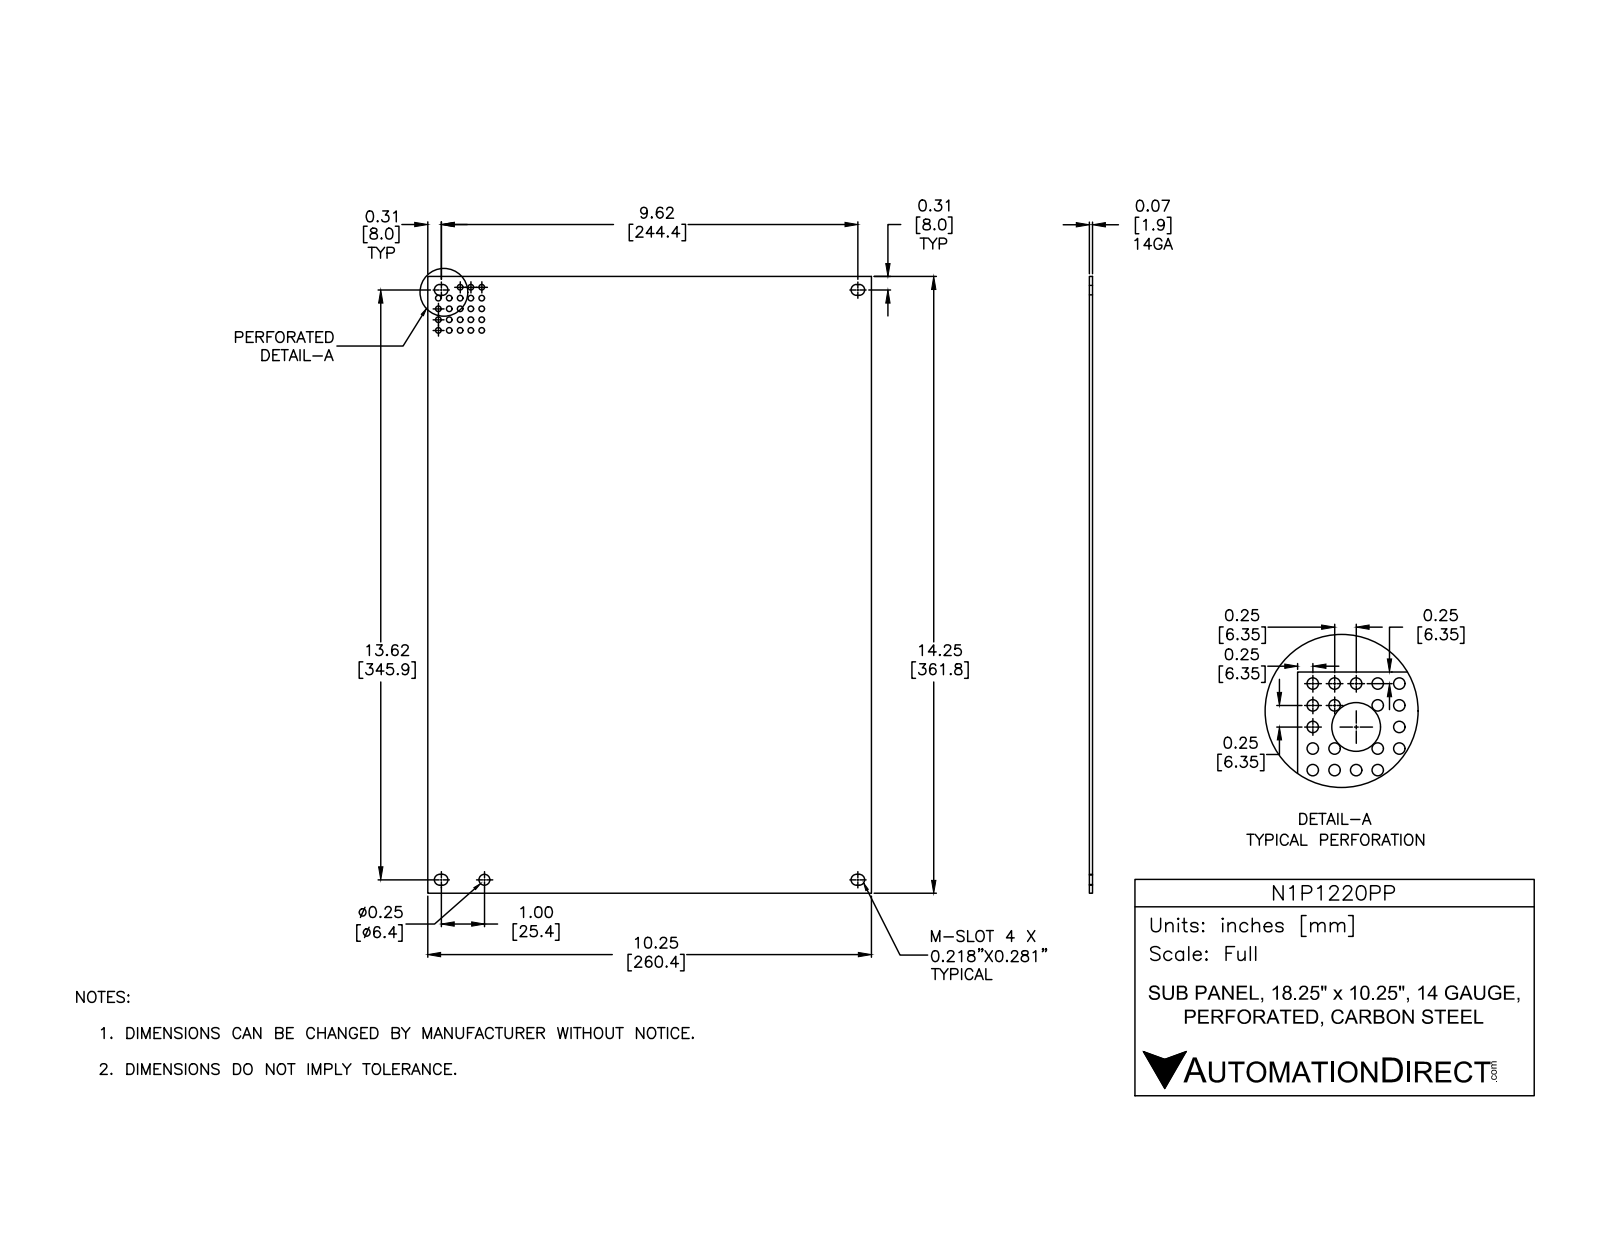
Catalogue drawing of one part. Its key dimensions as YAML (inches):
part_name: "N1P1220PP"
step_written_by: "Autodesk Inventor 2012 (AUTOMOTIVE_DESIGN)"
units: inches
bodies: {solids: 1, faces: 23, planar: 14, cylindrical: 9, other: 0}
overall_size: [18.25, 10.25, 0.074]
volume: 13.82
surface_area: 378.1
round_holes:
  - {diameter: 0.25, count: 1}
partial_cylinders:
  - {radius: 0.125, count: 8}
face_to_face_distances: [0.074, 10.25, 18.25, 0.438, 17.812, 0.188, 18.062, 0.25, 17.624, 17.374]
